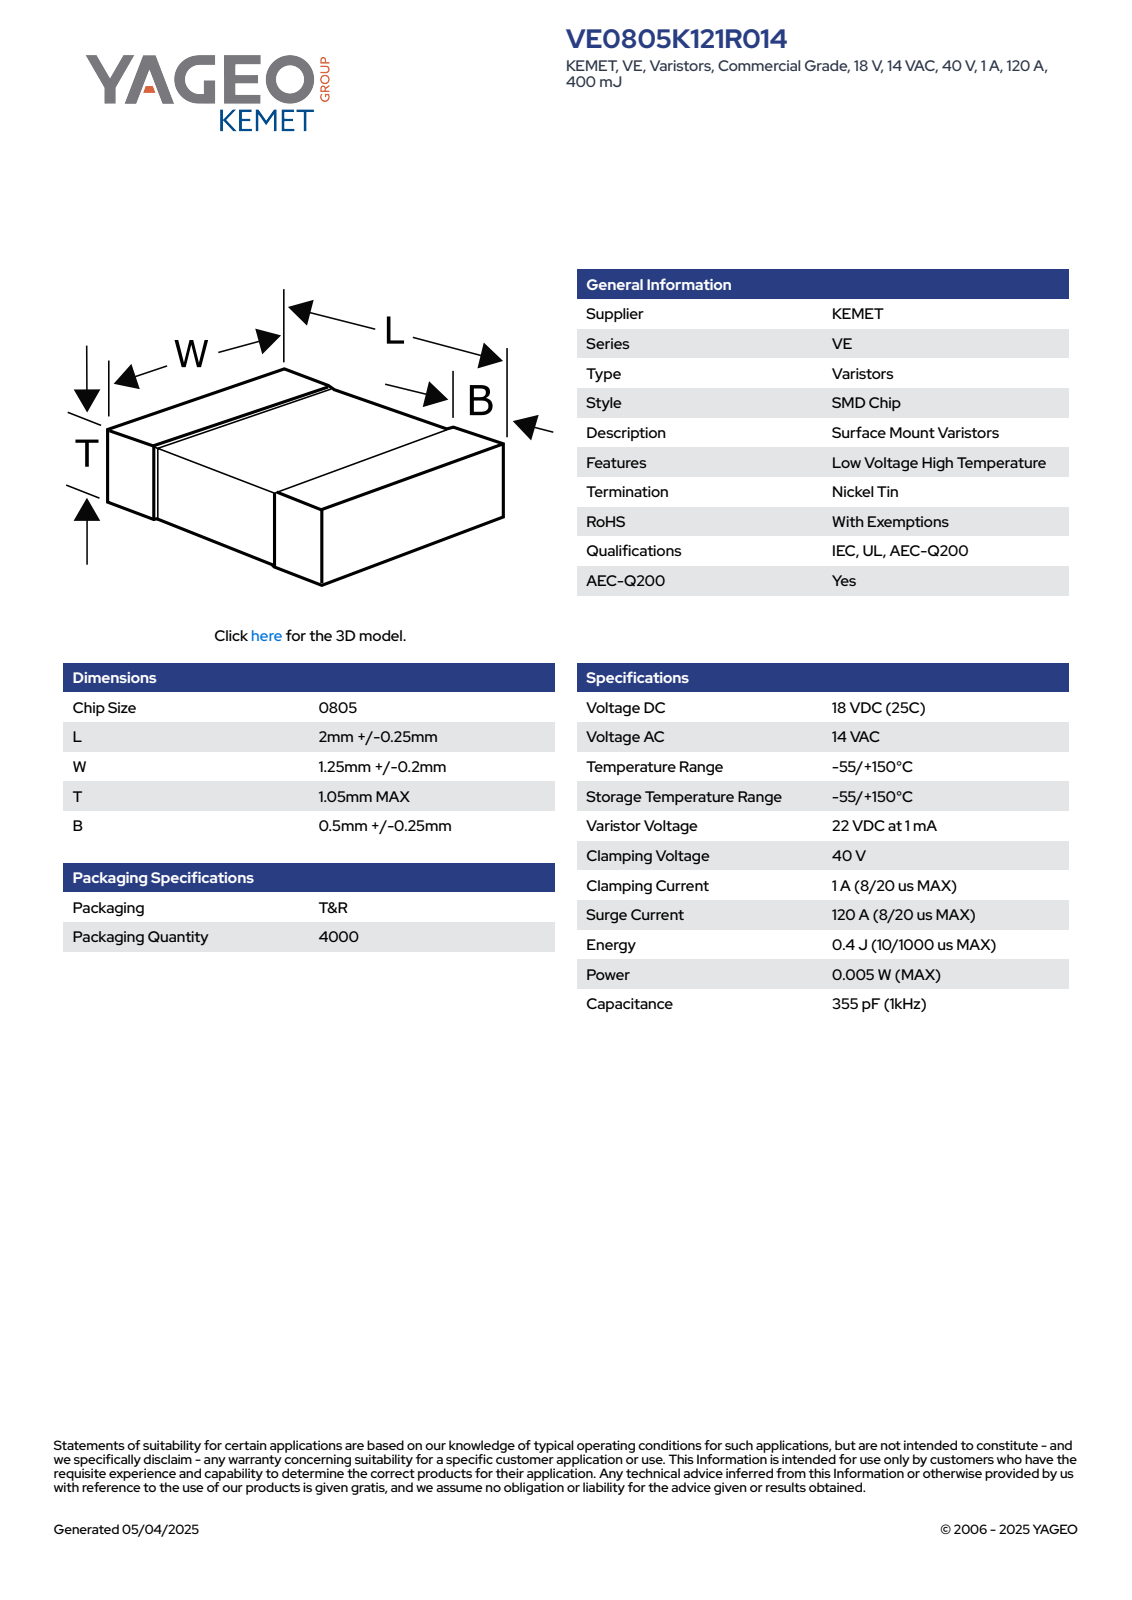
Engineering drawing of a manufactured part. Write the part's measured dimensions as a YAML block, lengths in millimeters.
part_name: "VS_SMD_0805_L2.25W1.45T0.8B0.75"
step_written_by: "SolidWorks 2014 (AUTOMOTIVE_DESIGN)"
units: millimeters
bodies: {solids: 4, faces: 129, planar: 71, cylindrical: 42, other: 16}
overall_size: [2.25, 1.45, 0.8]
volume: 3
surface_area: 12
face_to_face_distances: [0.77, 0.8, 2.25, 1.45, 1.42, 0.74, 1.39, 1, 1.25, 1.22]
